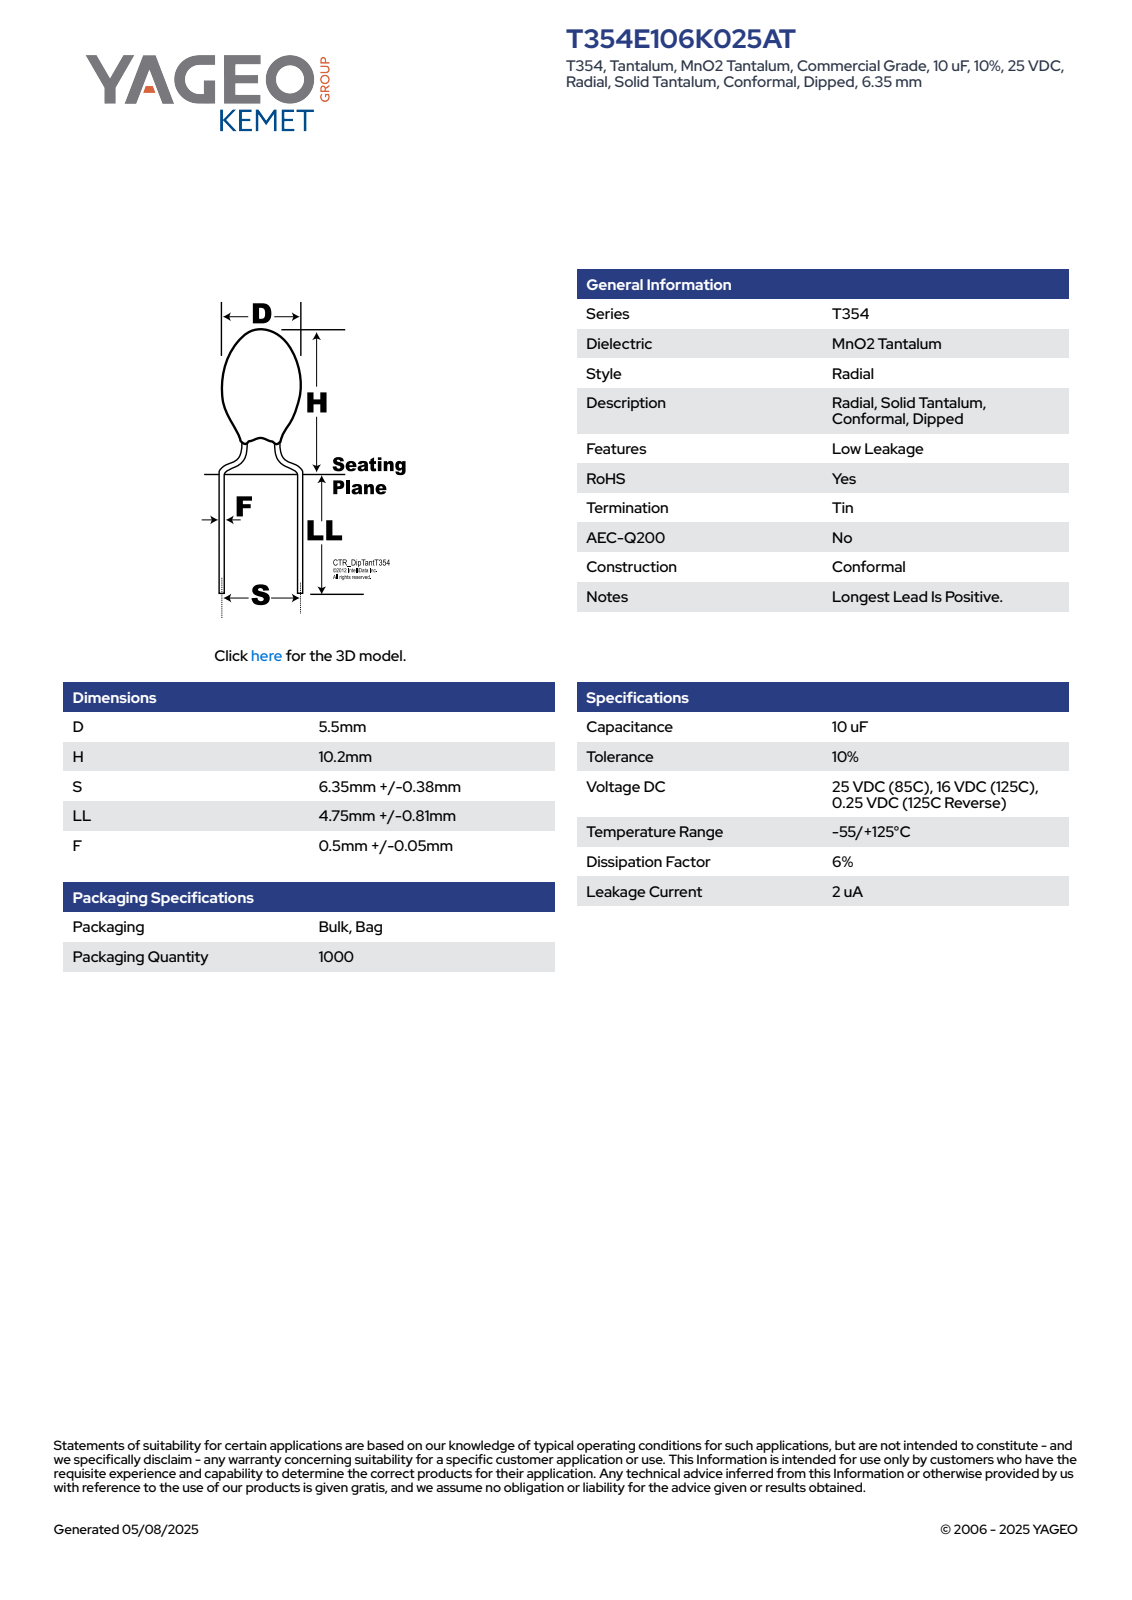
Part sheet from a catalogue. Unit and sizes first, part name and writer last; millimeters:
Units: millimetres
Overall size (bounding box): 15.76 × 6.9 × 5.5
Round bosses / shafts (diameter × count): ⌀0.55 ×2, ⌀5.5 ×1
Partial cylindrical surfaces — rounded edges, fillets, slot ends (radius × count): R2.74 ×1
Main face-to-face distances: 7.12, 8.64, 15.76, 13.28, 4.64, 2.48, 12.47, 3.83, 0.81, 3.29
Volume: 155 mm³ · Surface area: 178 mm²
Bodies: 1 solid, 81 faces (26 planar, 10 cylindrical, 45 other)
Part name (STEP PRODUCT): CTR_T354_D5.5H10.2S6.35LL5.56F0.55
STEP written by: SolidWorks 2014 (AUTOMOTIVE_DESIGN)
